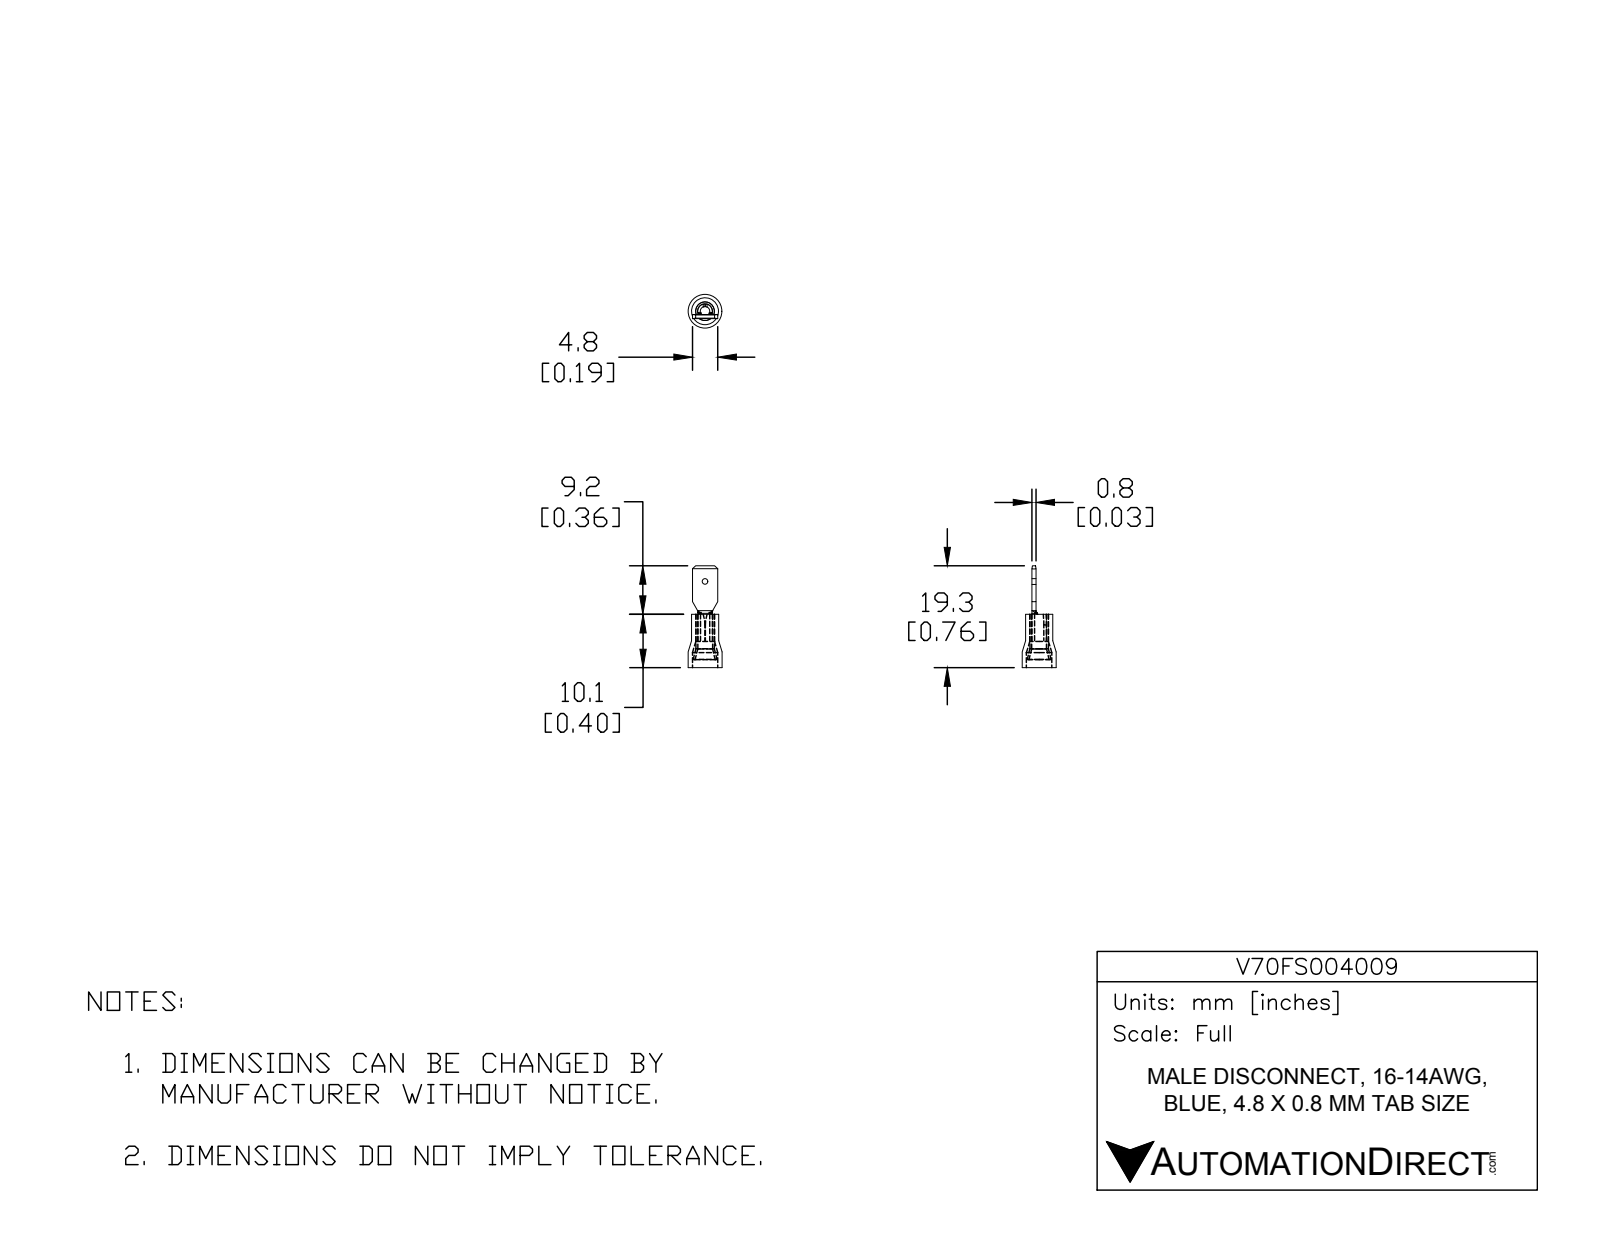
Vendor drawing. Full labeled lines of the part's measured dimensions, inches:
Part name (STEP PRODUCT): V70FS004009
STEP written by: SolidWorks 2017 (AUTOMOTIVE_DESIGN)
Units: inches
Bodies: 3 solids, 59 faces (19 planar, 22 cylindrical, 18 other)
Overall size (bounding box): 0.76 × 0.252 × 0.252
Volume: 0.012 in³ · Surface area: 1.09 in²
Round holes (diameter × count): ⌀0.043 ×1, ⌀0.069 ×1, ⌀0.11 ×1, ⌀0.139 ×1, ⌀0.189 ×1
Round bosses / shafts (diameter × count): ⌀0.252 ×1, ⌀0.202 ×1, ⌀0.138 ×1, ⌀0.109 ×1
Partial cylindrical surfaces — rounded edges, fillets, slot ends (radius × count): R0.232 ×2
Main face-to-face distances: 0.031, 0.398, 0.189, 0.201, 0.197, 0.093, 0.096, 0.76, 0.559, 0.362
